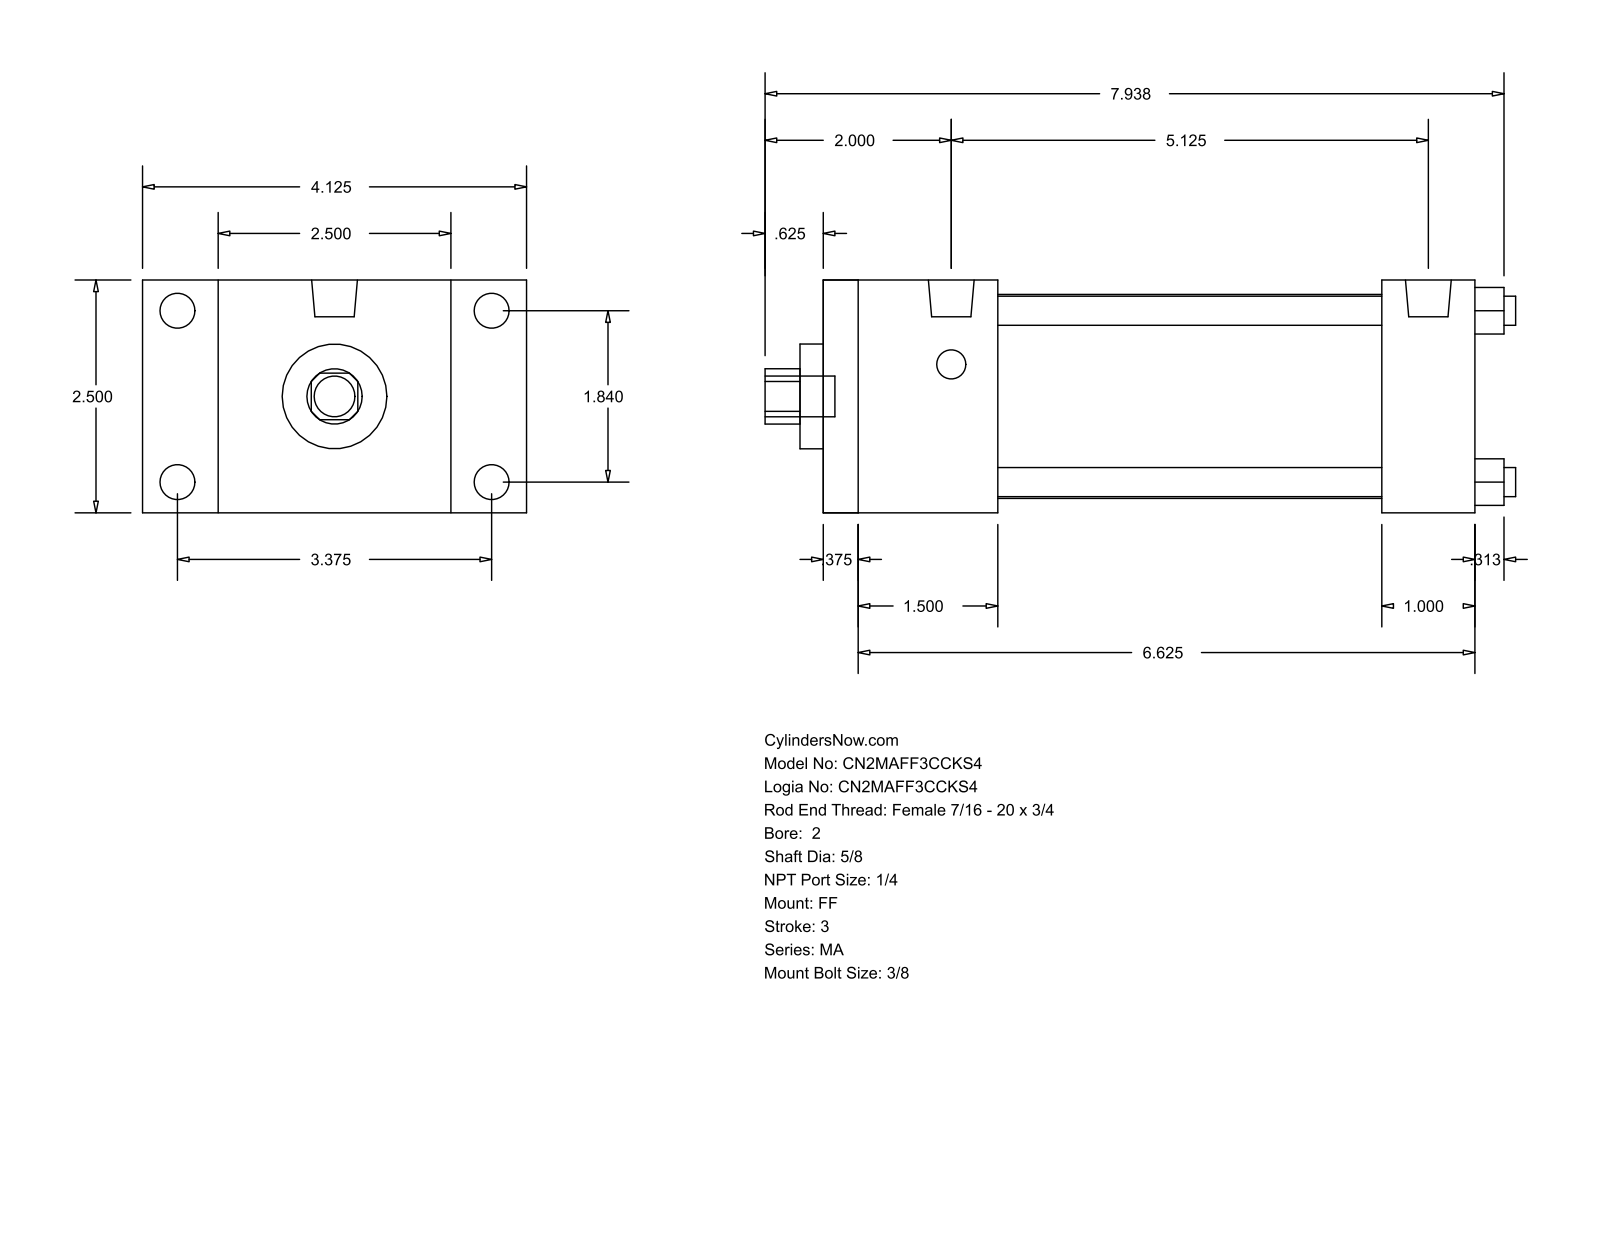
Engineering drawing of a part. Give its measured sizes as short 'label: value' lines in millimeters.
name: MA_FF__0200_0.625
written by: GSSL Pune (CONFIG_CONTROL_DESIGN)
unit: mm
bodies: 0 solids, 92 faces (64 planar, 28 cylindrical, 0 other)
size: 204.79 × 104.78 × 63.5
holes: 4× ⌀7.94, 1× ⌀15.88, 1× ⌀28.57, 1× ⌀55.63
bosses: 4× ⌀9.53, 4× ⌀7.94, 2× ⌀12.49, 1× ⌀11.11
rounds: 1× R7.54
face distances: 63.5, 177.8, 9.52, 168.28, 104.78, 25.4, 38.1, 47.62, 152.4, 142.88
hole spacings: 33.05, 46.74, 66.1
